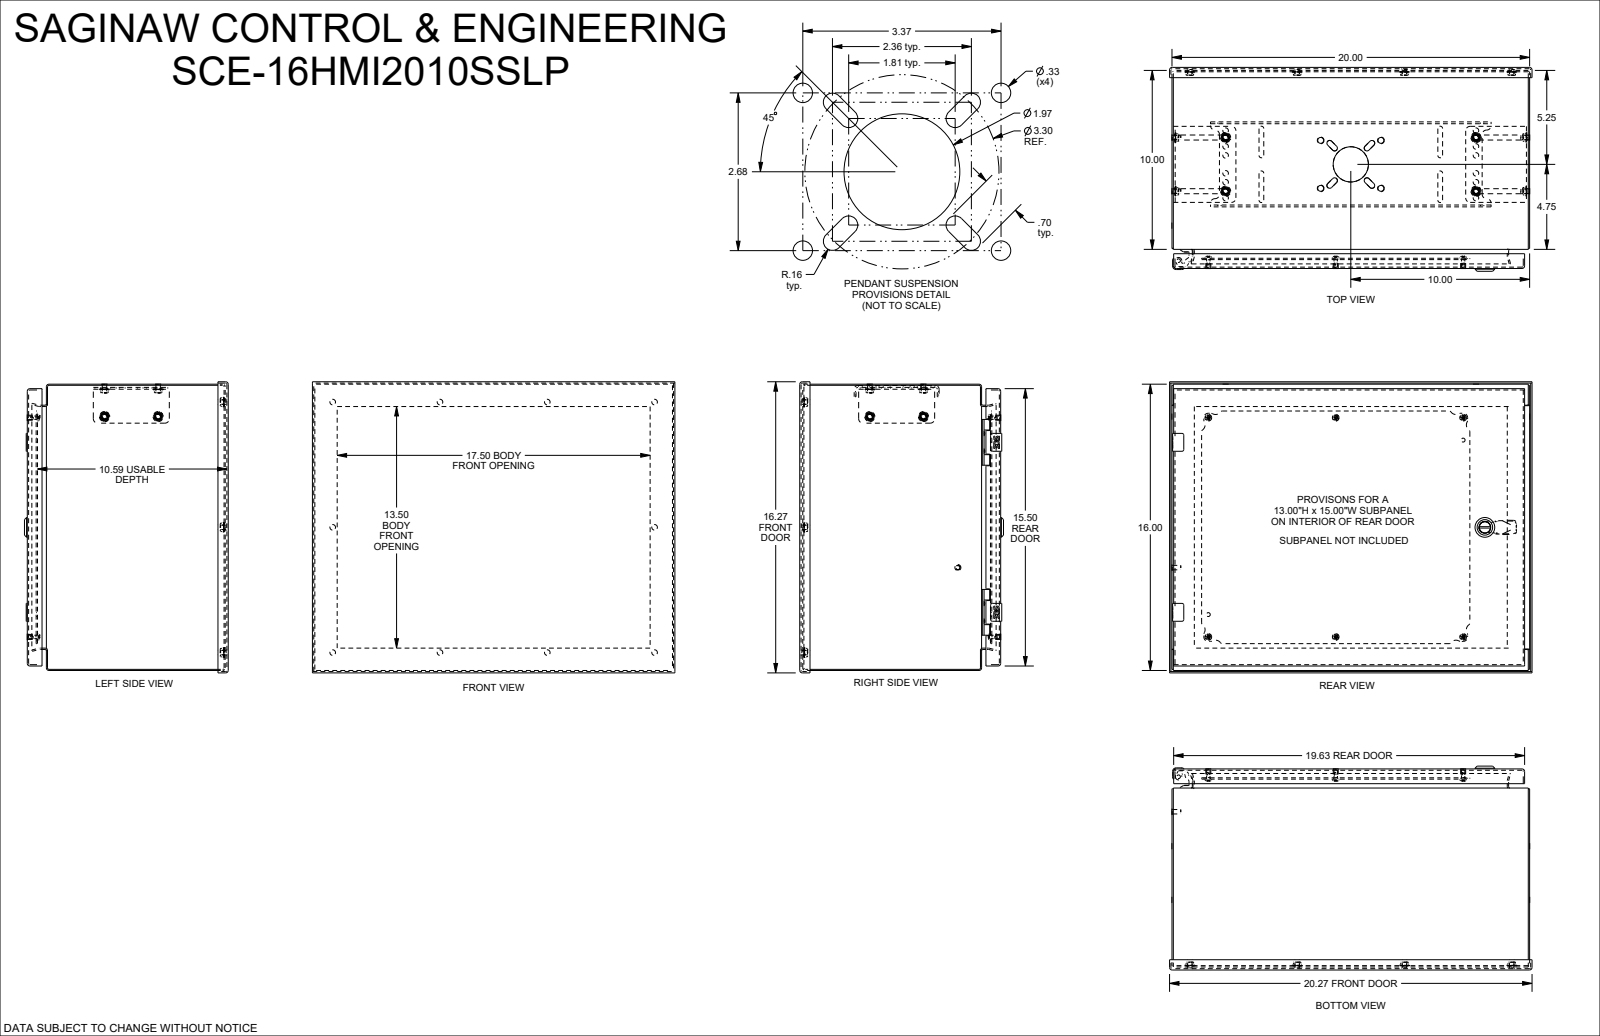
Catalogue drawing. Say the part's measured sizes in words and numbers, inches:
The part is named "SCE-16HMI2010LP". Its 3-D file was written by "SolidWorks 2023 (AUTOMOTIVE_DESIGN)". It is 24 solids with 2137 faces: 1050 planar, 698 cylindrical and 389 other. Overall it measures 20.27 by 16.27 by 11.395 inches. Its volume is 159.1 cubic inches and its surface area 3 996 square inches. Round holes: 12 of diameter 0.31, 10 of diameter 0.313, 7 of diameter 0.25, 6 of diameter 0.19, 6 of diameter 0.25, 4 of diameter 0.172, 4 of diameter 0.205, 4 of diameter 0.218, 4 of diameter 0.244, 4 of diameter 0.266, 4 of diameter 0.27, 4 of diameter 0.281. Round bosses or shafts: 17 of diameter 0.248, 7 of diameter 0.337, 6 of diameter 0.373, 6 of diameter 0.28, 6 of diameter 0.188, 6 of diameter 0.17, 4 of diameter 0.25, 4 of diameter 0.24. Partial cylindrical surfaces (rounded edges, fillets, slot ends): 30 of radius 0.012, 28 of radius 0.25, 24 of radius 0.015, 16 of radius 0.22, 13 of radius 0.06, 12 of radius 0.02, 12 of radius 0.1, 12 of radius 0.141. The main face-to-face distances are 0.075, 0.075, 10.667, 0.06, 11.163, 11.103, 11.178, 11.238, 0.496, 0.436. The hole center spacings are 14, 0.5, 14.009, 1, 2, 6, 9.5, 14.036.
